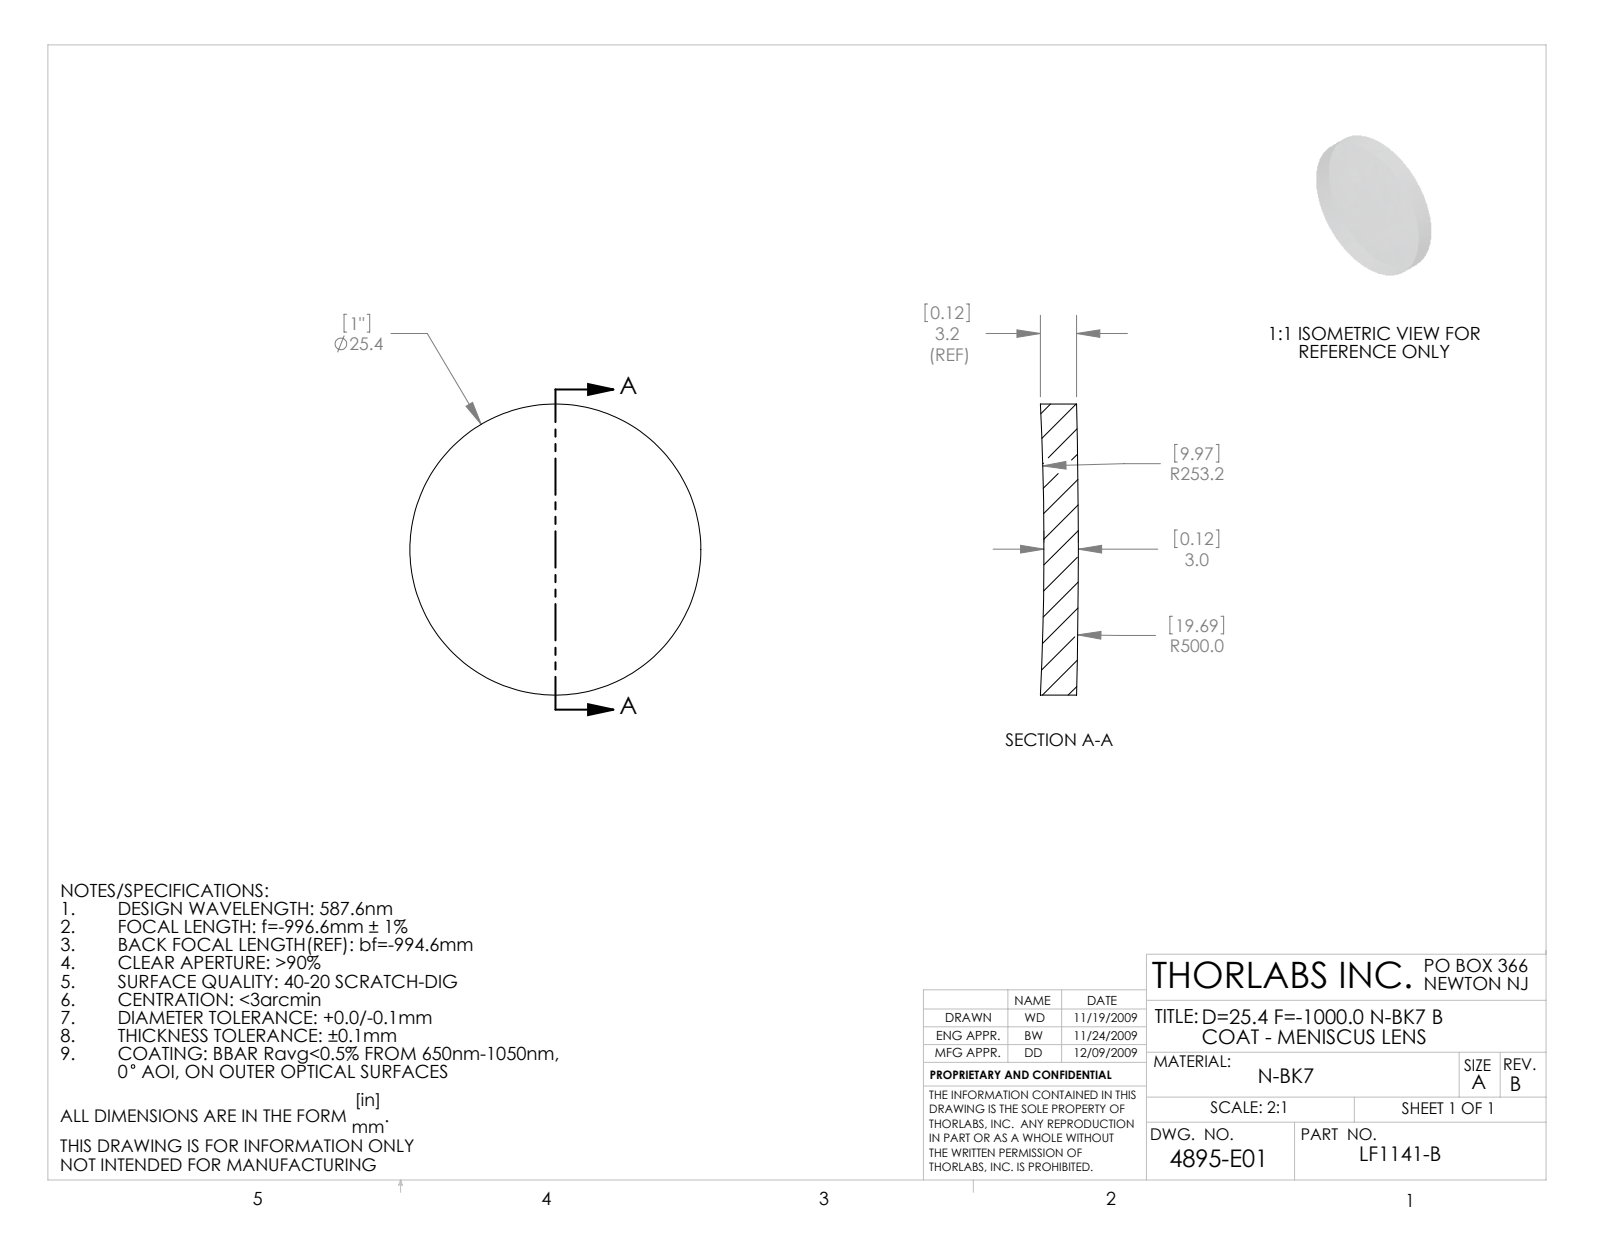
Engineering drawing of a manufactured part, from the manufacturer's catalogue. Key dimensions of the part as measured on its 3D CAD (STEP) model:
Part name (STEP PRODUCT): 4895-E0W
STEP written by: SolidWorks 2009 (AUTOMOTIVE_DESIGN)
Units: millimetres
Bodies: 1 solid, 6 faces (0 planar, 2 cylindrical, 4 other)
Overall size (bounding box): 25.4 × 25.4 × 3.32
Volume: 1 560 mm³ · Surface area: 1 266 mm²
Round bosses / shafts (diameter × count): ⌀25.4 ×1
